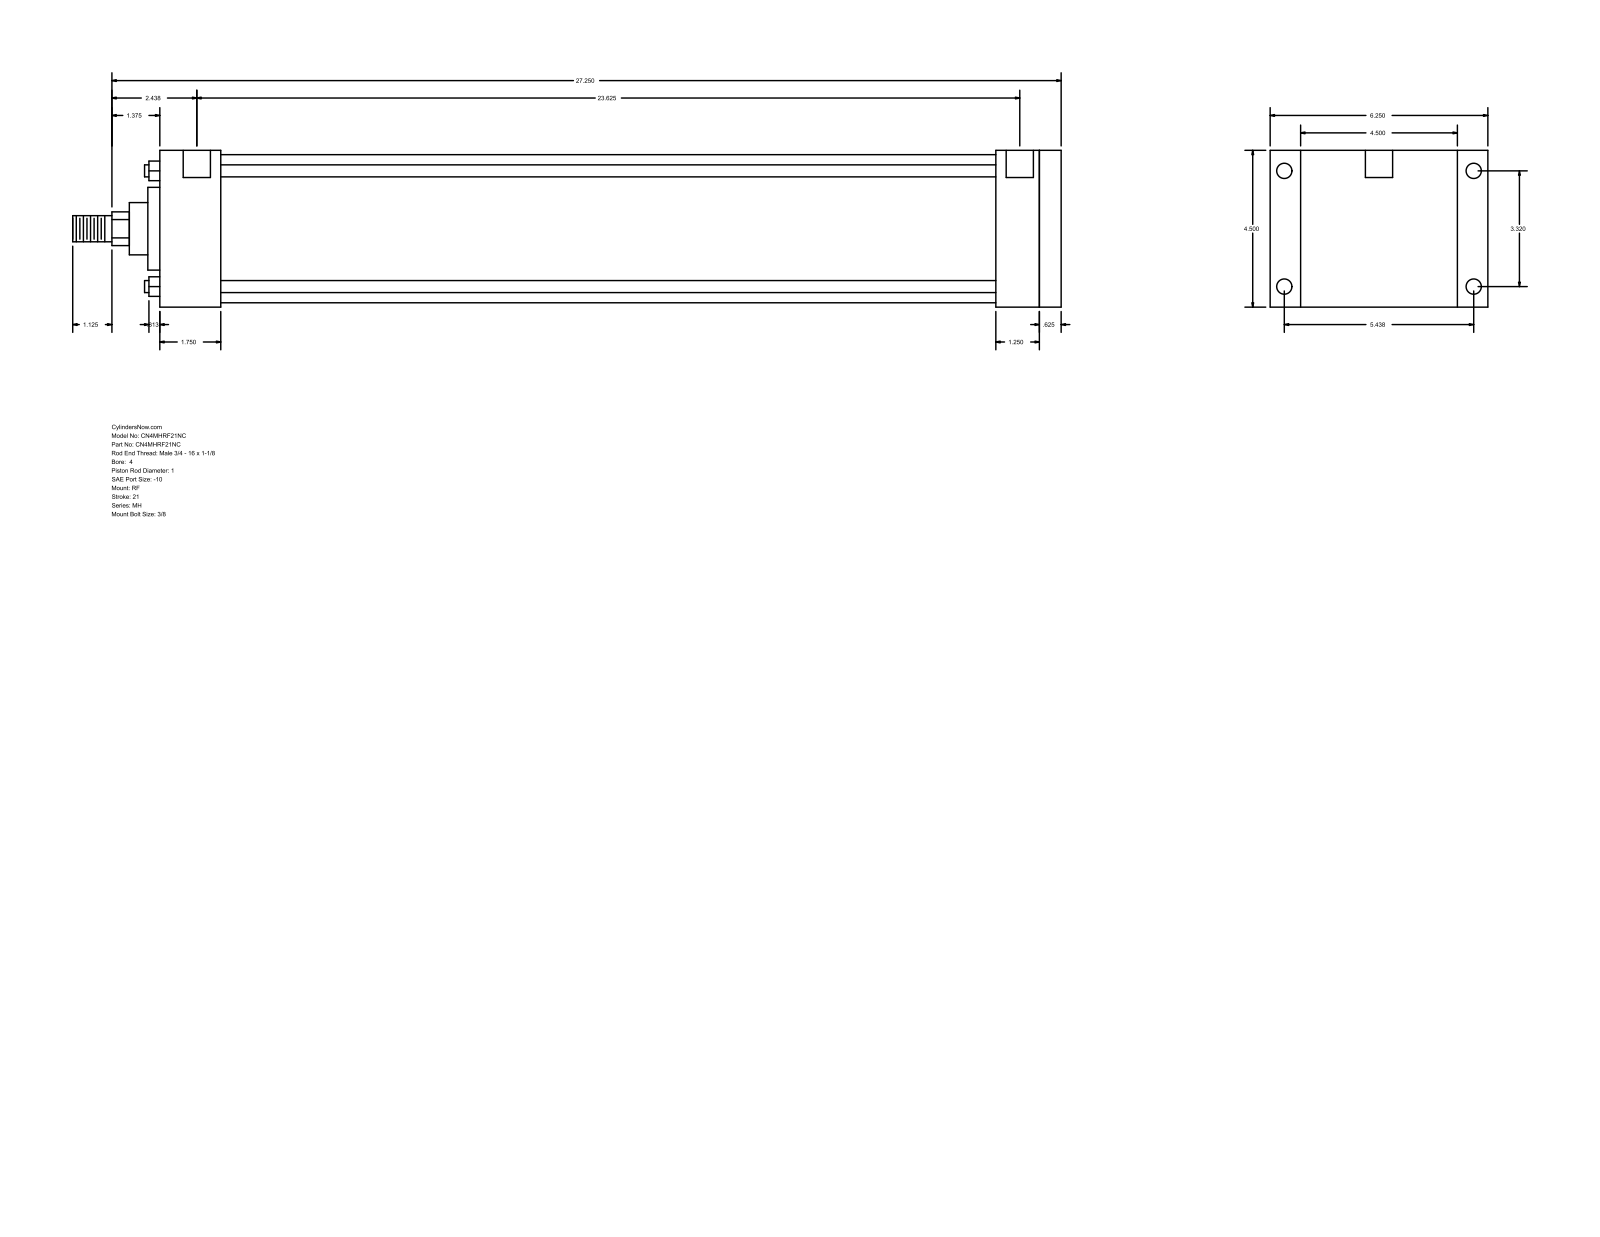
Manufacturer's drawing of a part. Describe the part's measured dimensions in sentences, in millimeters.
The part is named "MH_RF__0400_1". Its 3-D file was written by "GSSL Pune (CONFIG_CONTROL_DESIGN)". It is 0 solids with 94 faces: 65 planar, 29 cylindrical and 0 other. Overall it measures 720.73 by 158.75 by 114.3 millimeters. Round holes: 4 of diameter 8.73, 4 of diameter 11.13, 2 of diameter 19.84. Round bosses or shafts: 4 of diameter 8.76, 1 of diameter 107.95, 1 of diameter 60.33, 1 of diameter 38.1, 1 of diameter 25.4, 1 of diameter 19.05. Partial cylindrical surfaces (rounded edges, fillets, slot ends): 1 of radius 12.29. The main face-to-face distances are 114.3, 657.23, 641.35, 15.88, 47.63, 44.46, 596.89, 612.77, 609.6, 565.14. The hole center spacings are 84.32, 138.12, 161.82, 603.25, 1.58, 1.59, 600.08, 601.66.
